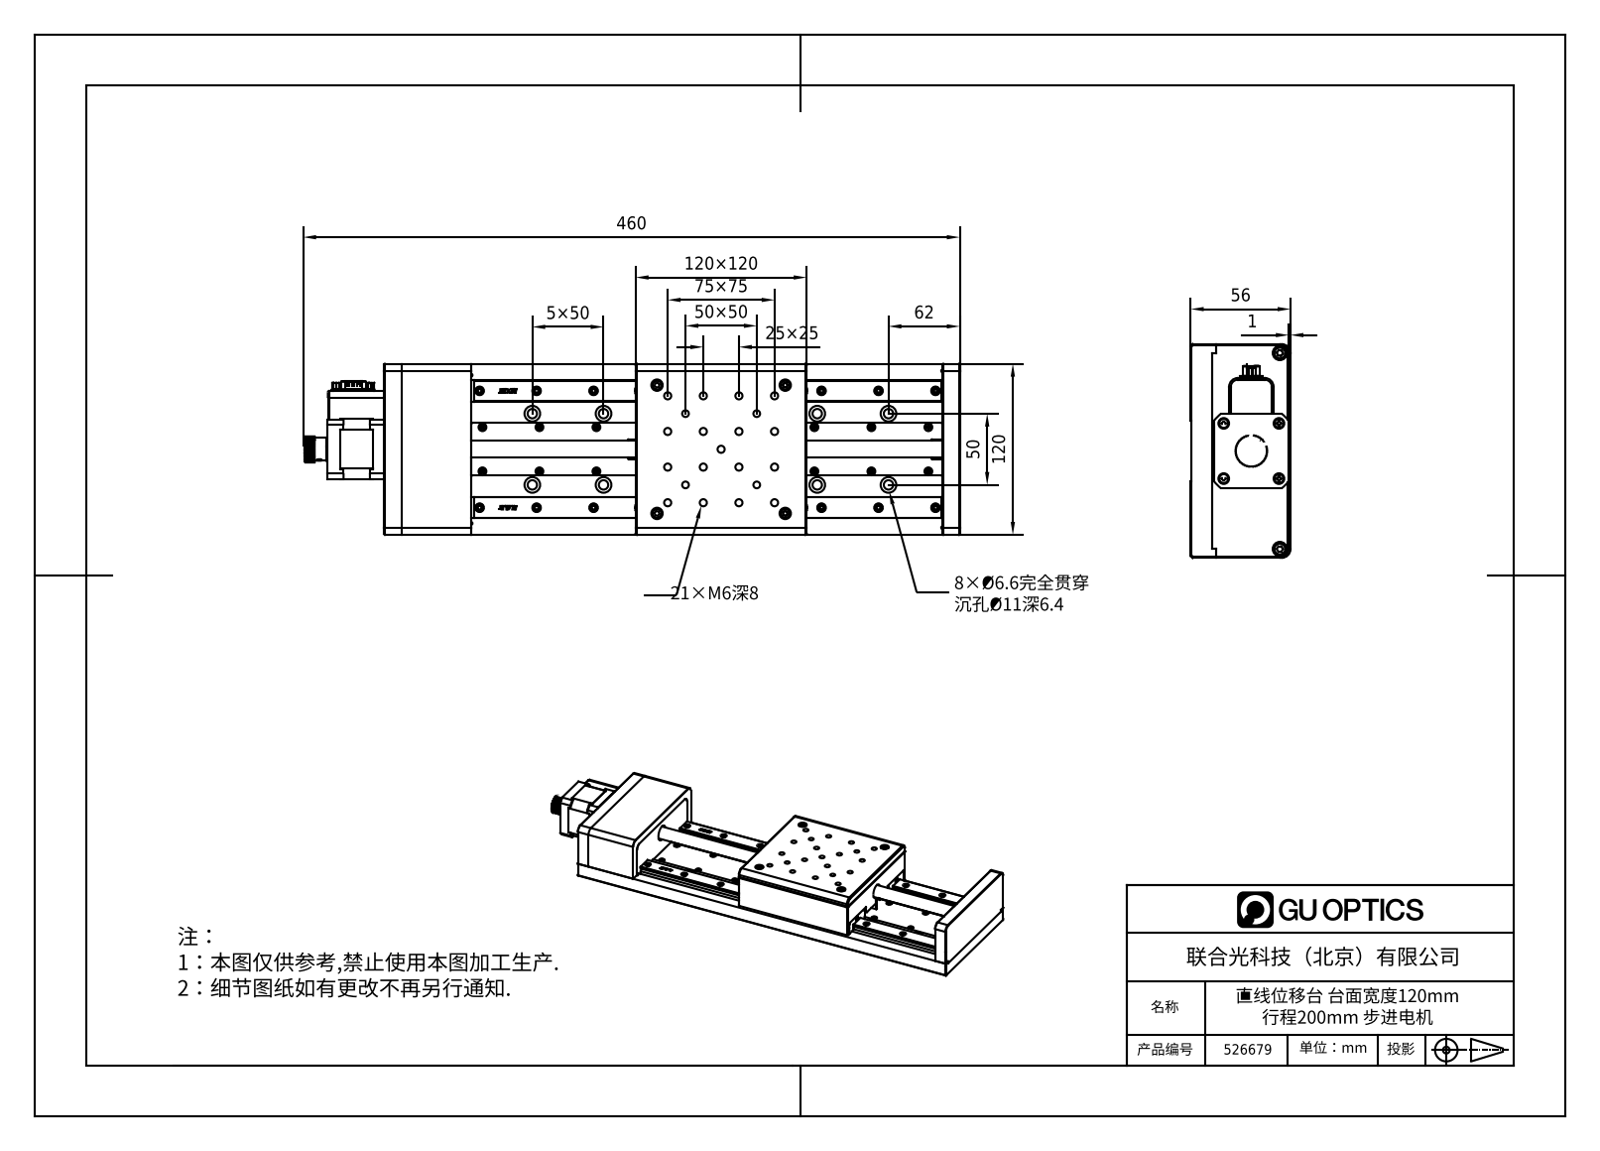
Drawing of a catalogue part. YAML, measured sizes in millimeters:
part_name: "FMS120V-200"
step_written_by: "SolidWorks 2017 (CONFIG_CONTROL_DESIGN)"
units: millimeters
bodies: {solids: 0, faces: 939, planar: 464, cylindrical: 288, other: 187}
overall_size: [452, 120, 56]
round_holes:
  - {diameter: 5, count: 17}
  - {diameter: 8, count: 14}
  - {diameter: 6, count: 12}
  - {diameter: 6.6, count: 12}
  - {diameter: 11, count: 6}
  - {diameter: 2, count: 4}
  - {diameter: 4.71, count: 4}
  - {diameter: 2.5, count: 2}
  - {diameter: 4.5, count: 2}
  - {diameter: 14, count: 1}
round_bosses_or_shafts:
  - {diameter: 4.4, count: 12}
  - {diameter: 1, count: 9}
  - {diameter: 5.5, count: 4}
  - {diameter: 7, count: 2}
  - {diameter: 4.2, count: 2}
  - {diameter: 12, count: 1}
partial_cylinders:
  - {radius: 0.5, count: 24}
  - {radius: 1, count: 10}
  - {radius: 0.3, count: 7}
  - {radius: 0.4, count: 7}
  - {radius: 5, count: 6}
  - {radius: 1.5, count: 4}
  - {radius: 20, count: 1}
  - {radius: 20.5, count: 1}
face_to_face_distances: [34, 48, 14, 8, 28, 42, 120, 13.7, 47.7, 56]
hole_center_spacings: [50, 70.71, 100, 111.8, 150, 158.11, 90, 200]
